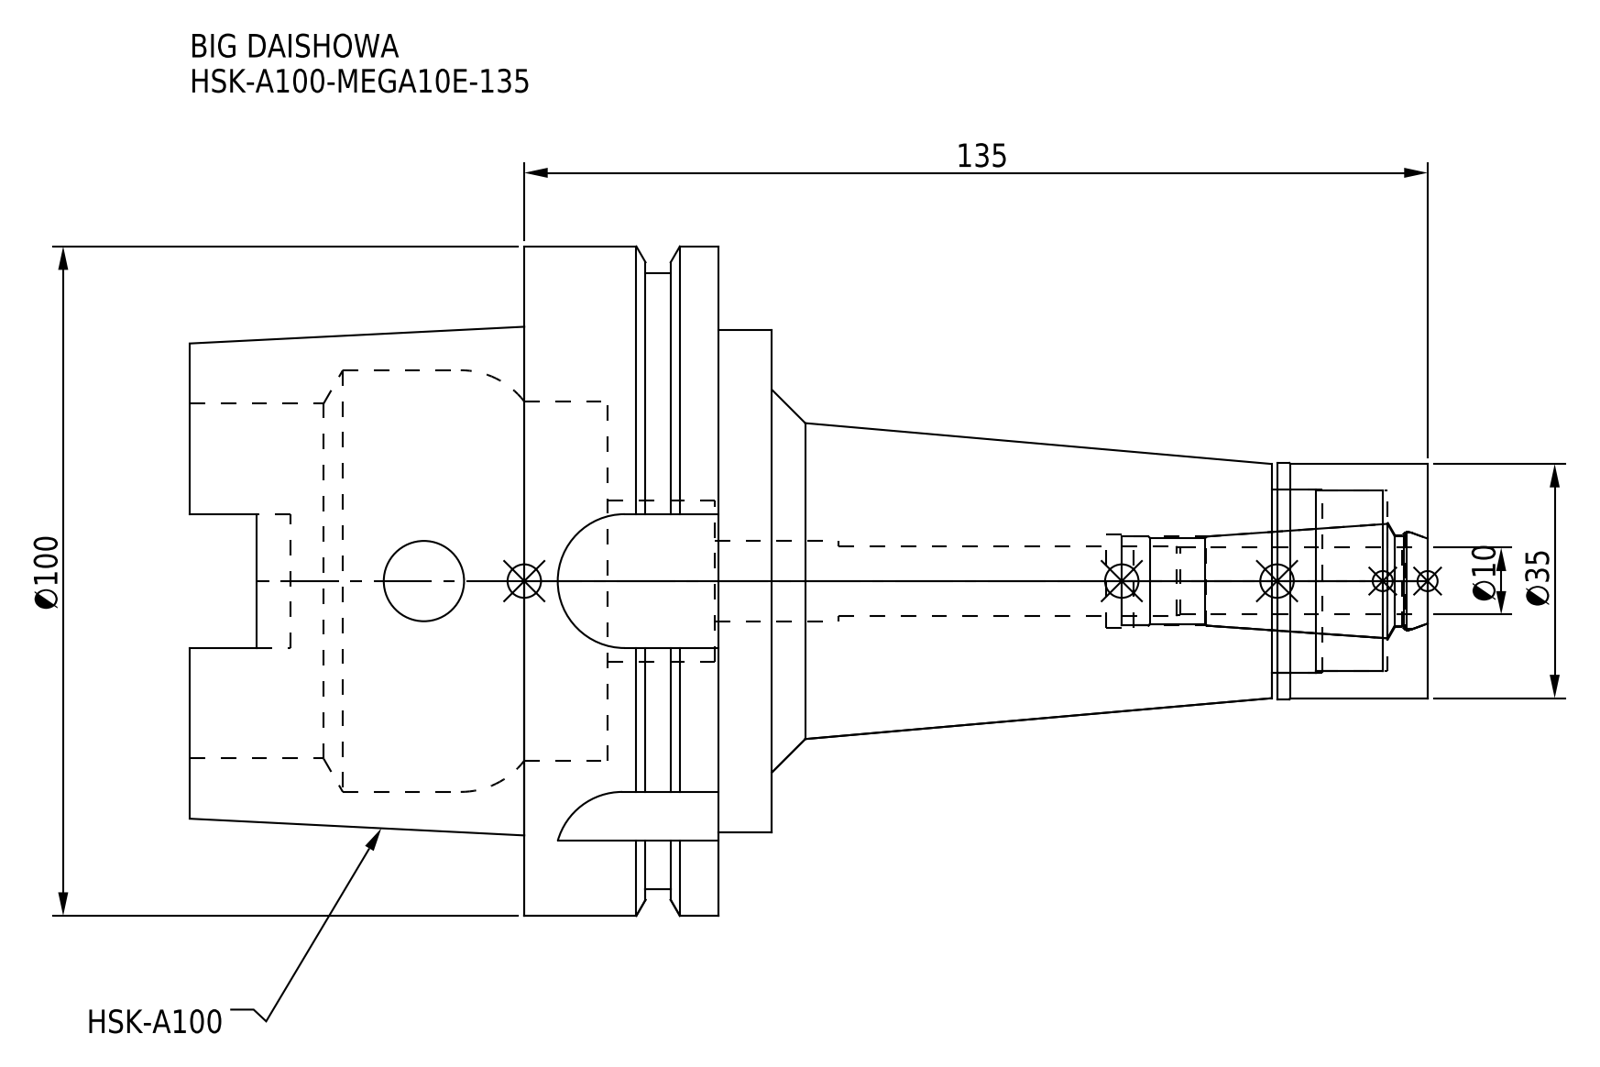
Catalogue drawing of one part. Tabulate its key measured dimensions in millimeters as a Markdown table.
| quantity | value |
| --- | --- |
| part name | HSK-A100-MEGA10E-135-100-FreeParts; HSK-A100-MEGA10E-135-100.stp; HSK-A100-MEGA10E-135_1.stp; HSK-A100-MEGA10E-135 (+3 more) |
| STEP written by | SolidWorks 2019 (CONFIG_CONTROL_DESIGN) |
| units | millimeters |
| bodies | 2 solids, 126 faces (42 planar, 56 cylindrical, 28 other) |
| overall size | 185 × 100 × 100 |
| volume | 401 205 mm³ |
| surface area | 71 354 mm² |
| round holes (diameter × count) | 12 × 2, 10.4 × 1, 13.3 × 1, 13.8 × 1, 13.9 × 1, 14.7 × 1, 24 × 1, 27 × 1, 27.5 × 1, 53 × 1, 53.8 × 1, 63 × 1 |
| round bosses / shafts (diameter × count) | 100 × 1, 92 × 1, 75 × 1, 35.3 × 1, 35 × 1 |
| partial cylindrical surfaces (radius × count) | 4.88 × 4, 10 × 4 |
| main face-to-face distances | 29, 8, 37, 24.55, 16.55, 12.45, 87, 50, 79, 62.45 |
